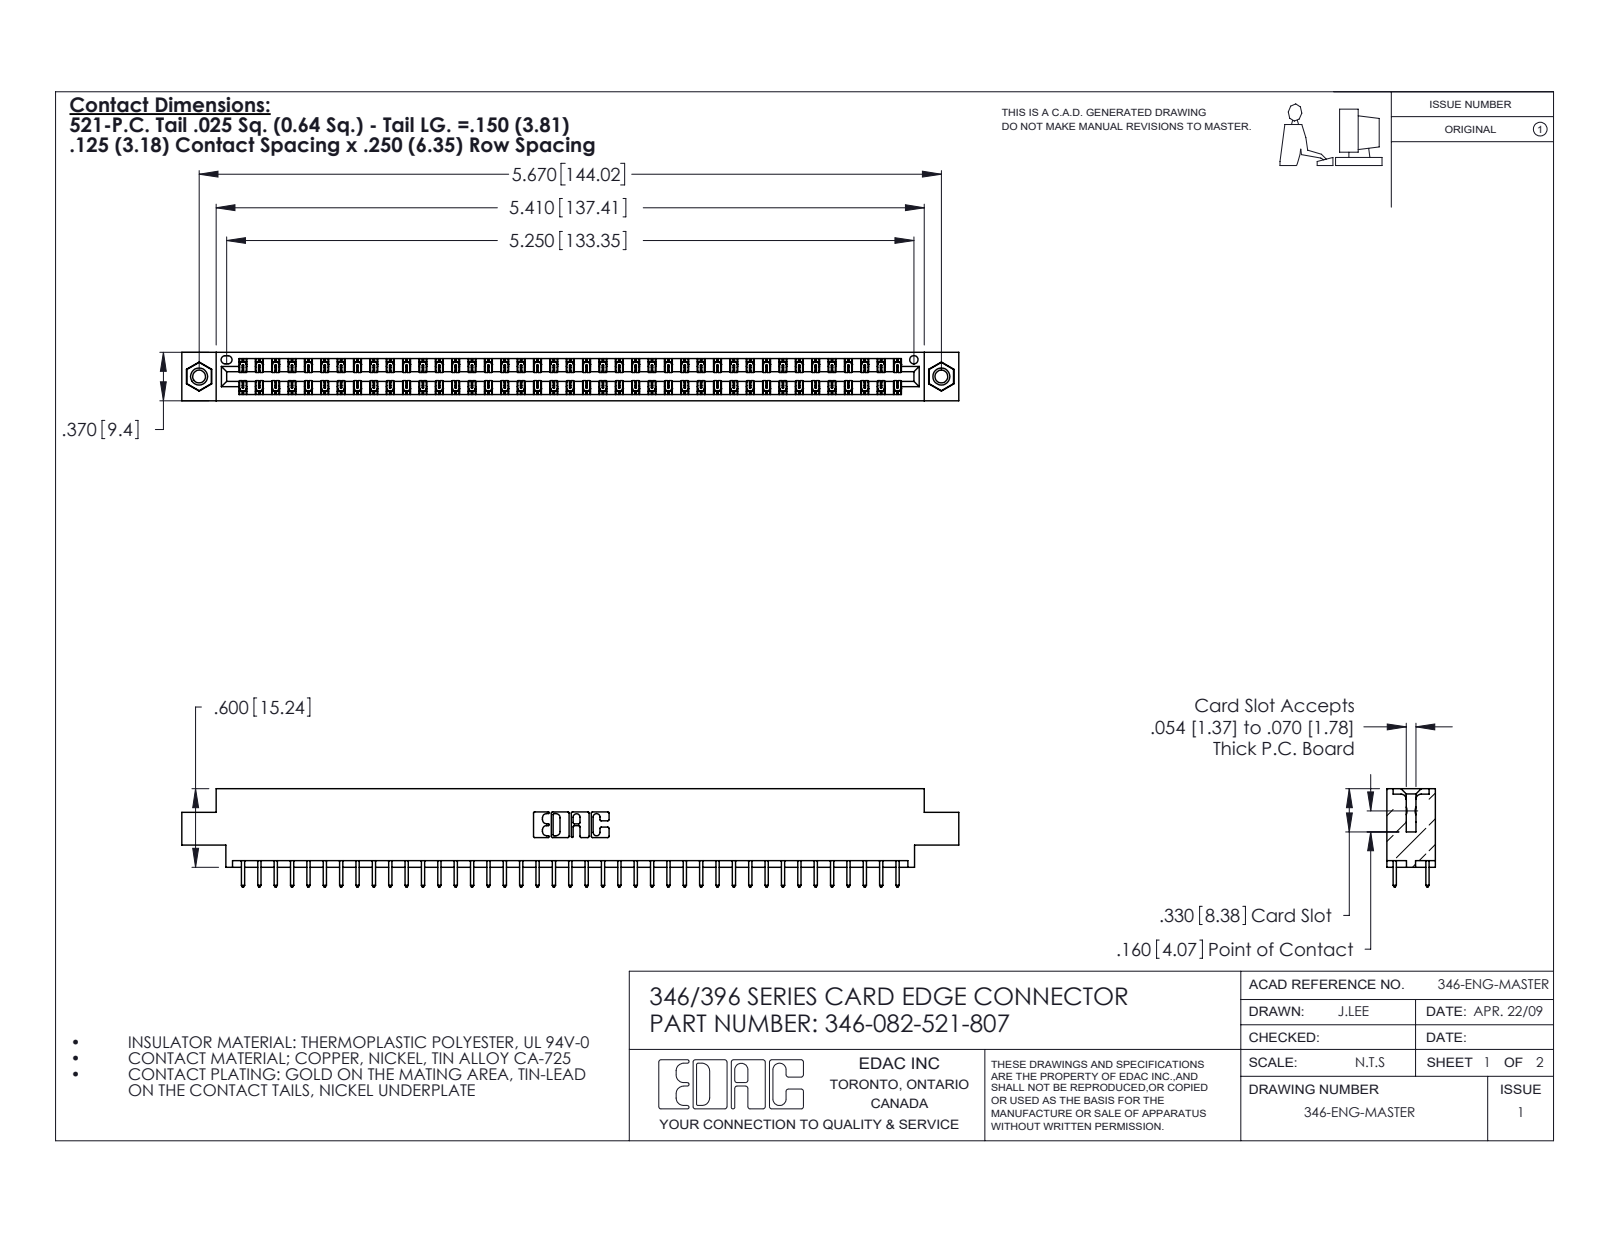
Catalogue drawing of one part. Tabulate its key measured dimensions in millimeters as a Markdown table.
| quantity | value |
| --- | --- |
| part name | 345-250-001_345-250-005-103; 346-082-521-807; 346 Part_0.170 Offset - 0.156 Dia-TI; 345-292-001_345-293-121 |
| STEP written by | SolidWorks 2020 (CONFIG_CONTROL_DESIGN) |
| units | millimeters |
| bodies | 85 solids, 4450 faces (2982 planar, 1452 cylindrical, 16 other) |
| overall size | 150.7 × 19.1 × 9.4 |
| volume | 14 500 mm³ |
| surface area | 19 890 mm² |
| round holes (diameter × count) | 2.5 × 2, 3.2 × 2, 4 × 2, 1.6 × 1 |
| round bosses / shafts (diameter × count) | 3.9 × 2 |
| partial cylindrical surfaces (radius × count) | 0.2 × 123, 0.3 × 82, 0.3 × 22, 0.2 × 6, 0.8 × 6, 0.7 × 3, 0.4 × 2, 0.6 × 2 |
| main face-to-face distances | 1.2, 8.2, 9.4, 6.4, 1.8, 7.6, 0.6, 7, 5.6, 3.8 |
| hole center spacings | 6.2, 138.7, 144 |
